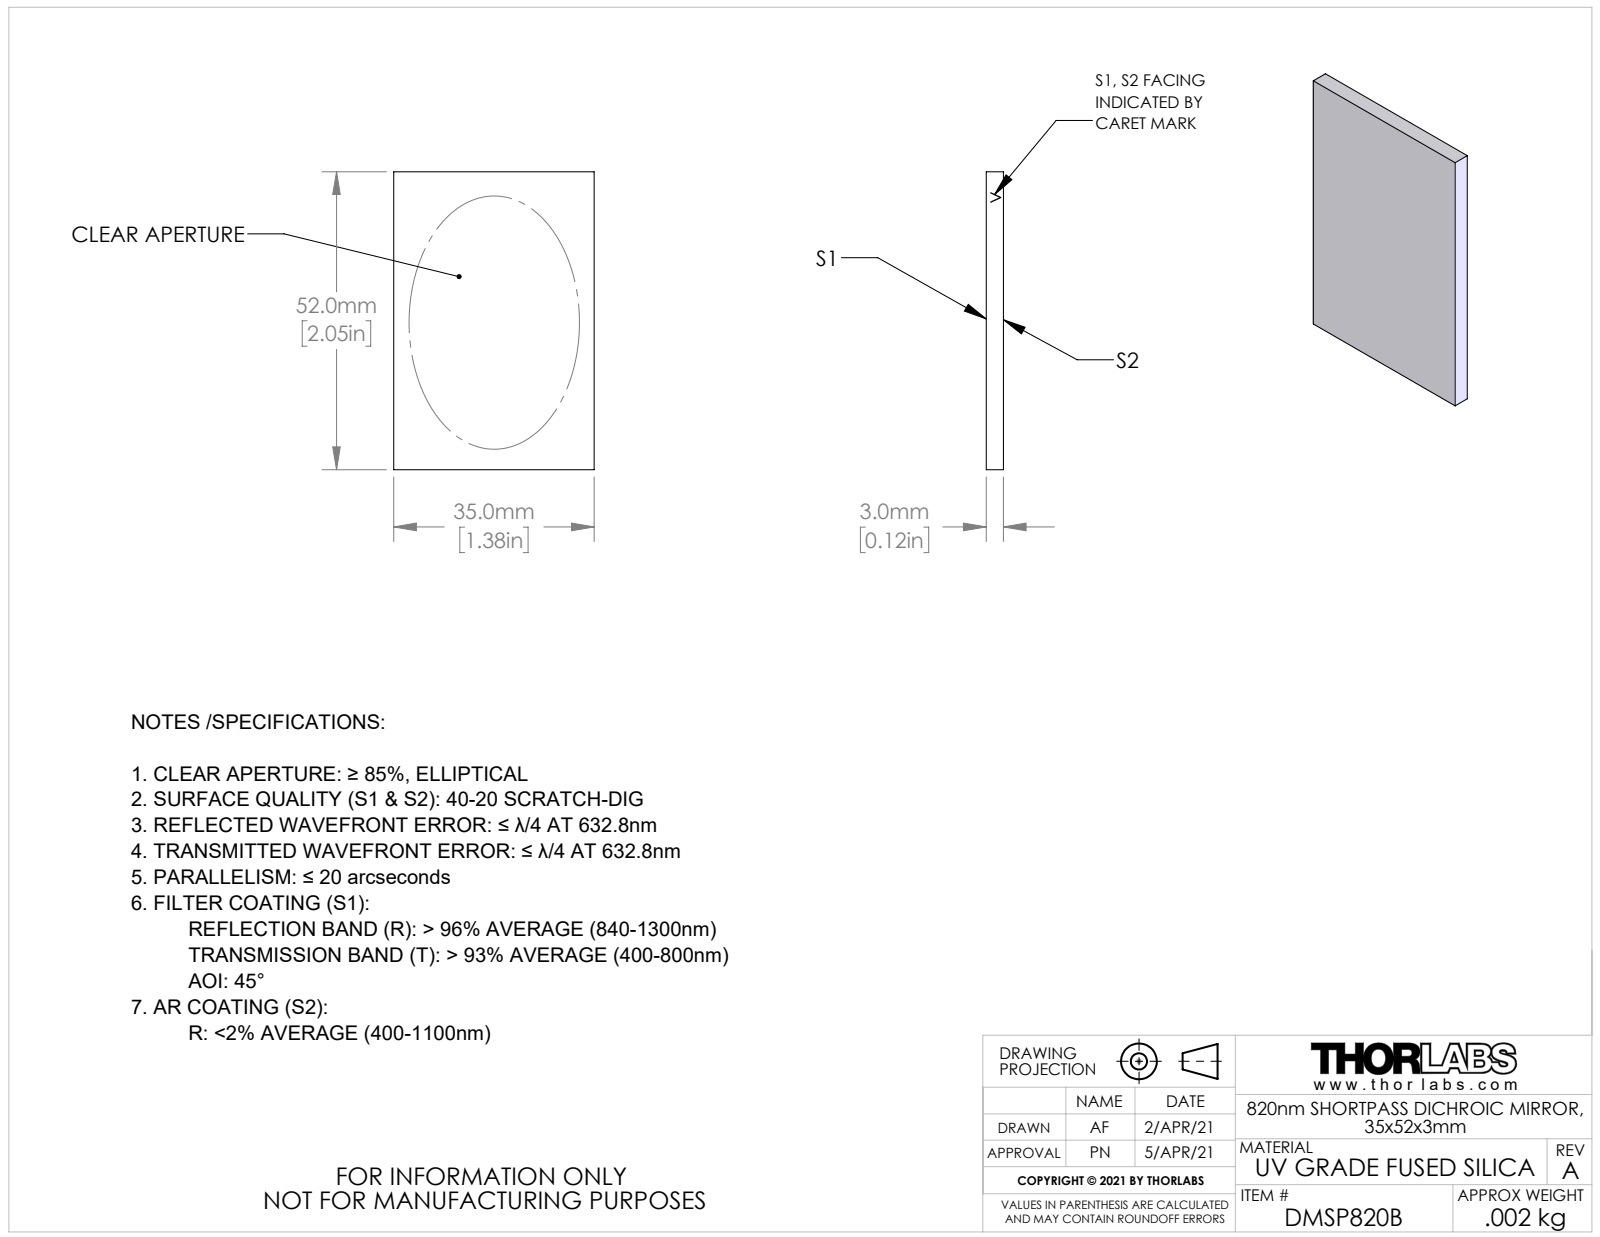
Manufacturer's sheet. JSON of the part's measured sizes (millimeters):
{"part_name": "TTN233919-E0W", "step_written_by": "SolidWorks 2018 (AUTOMOTIVE_DESIGN)", "units": "millimeters", "bodies": {"solids": 1, "faces": 6, "planar": 6, "cylindrical": 0, "other": 0}, "overall_size": [52, 35, 3], "volume_mm3": 5460, "surface_area_mm2": 4162, "face_to_face_distances": [3, 35, 52]}
